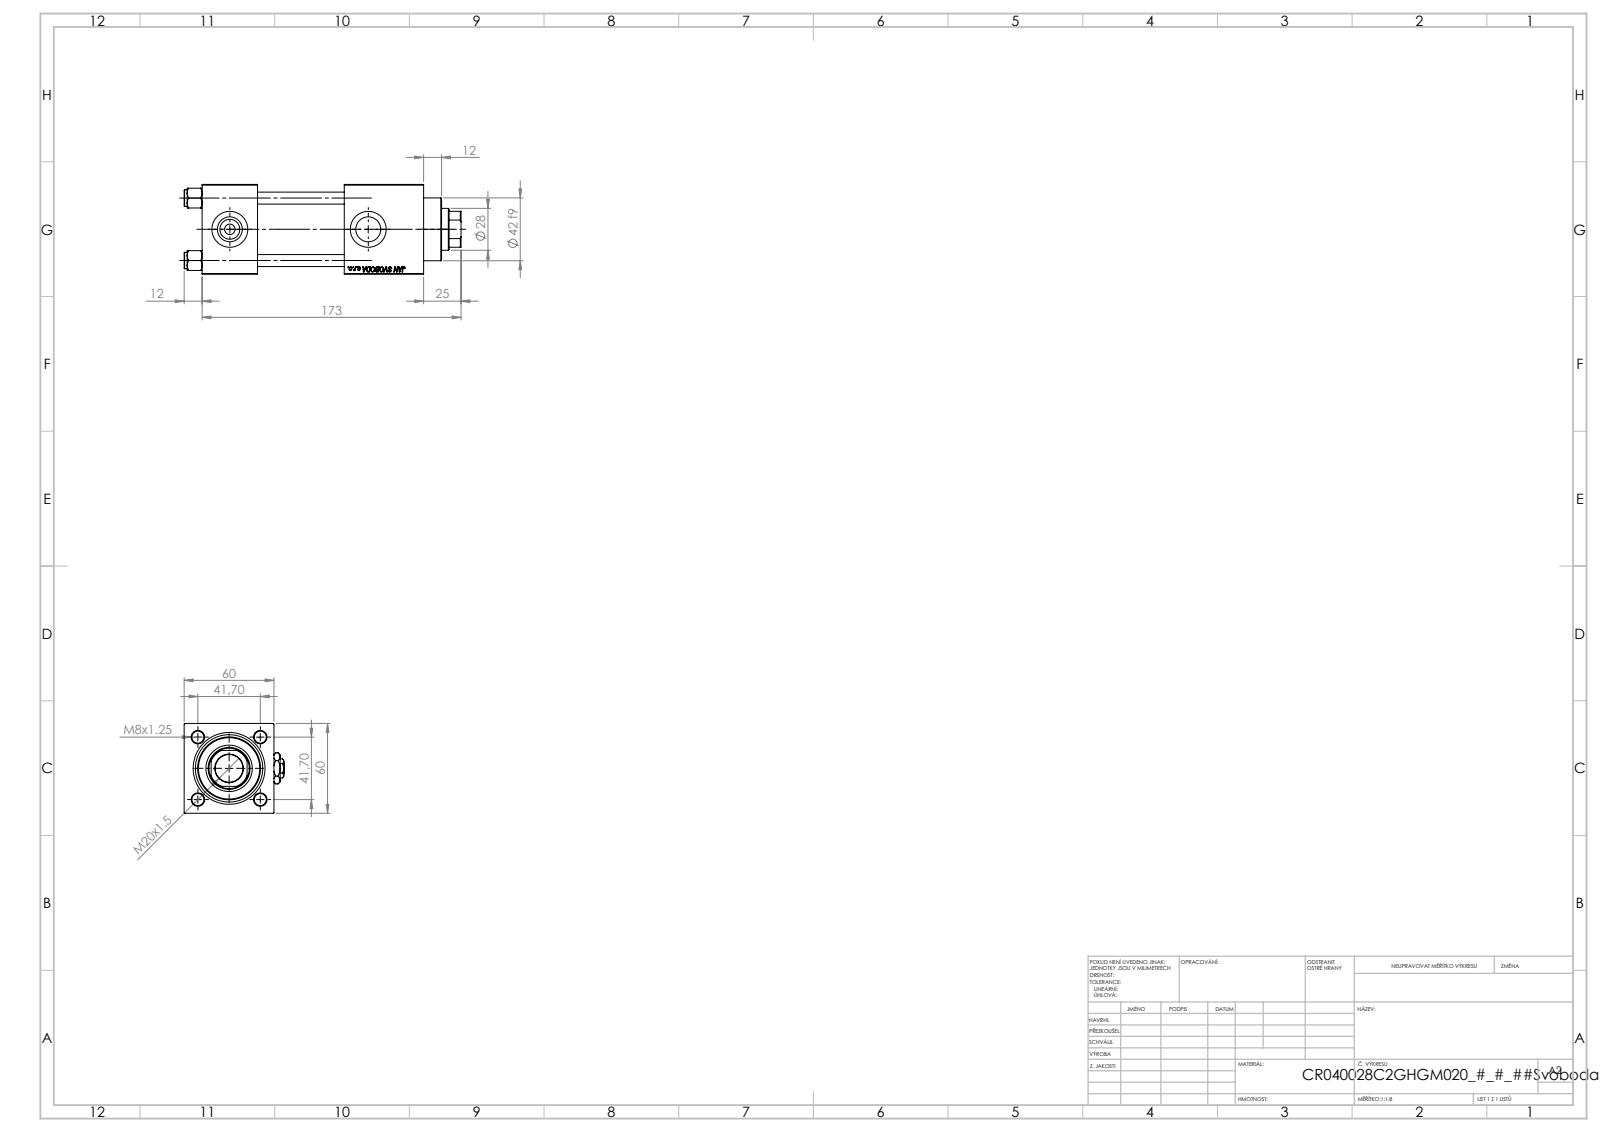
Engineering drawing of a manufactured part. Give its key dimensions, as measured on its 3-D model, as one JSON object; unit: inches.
{"part_name": "V215_VC_A; Zatka_pro_OIL_PORT; V215CR_C_TYCINKA; V215CR_C_Body (+2 more)", "step_written_by": "SolidWorks 2019 (CONFIG_CONTROL_DESIGN)", "units": "inches", "bodies": {"solids": 12, "faces": 1202, "planar": 550, "cylindrical": 94, "other": 558}, "overall_size": [7.283, 2.638, 2.362], "volume_in3": 25.8, "surface_area_in2": 175.3, "round_holes": [[0.315, 4], [0.276, 2], [0.656, 2], [0.945, 2], [0.728, 1], [1.102, 1], [1.22, 1], [1.575, 1], [1.772, 1]], "round_bosses_or_shafts": [[0.433, 4], [1.811, 1], [1.654, 1]], "partial_cylinders_radius": [[0.531, 1]], "face_to_face_distances": [2.362, 1.457, 2.283, 3.74, 2.087, 4.697, 3.24, 0.957, 5.827, 4.37], "hole_center_spacings": [1.161, 1.642, 2.322, 3.642]}
